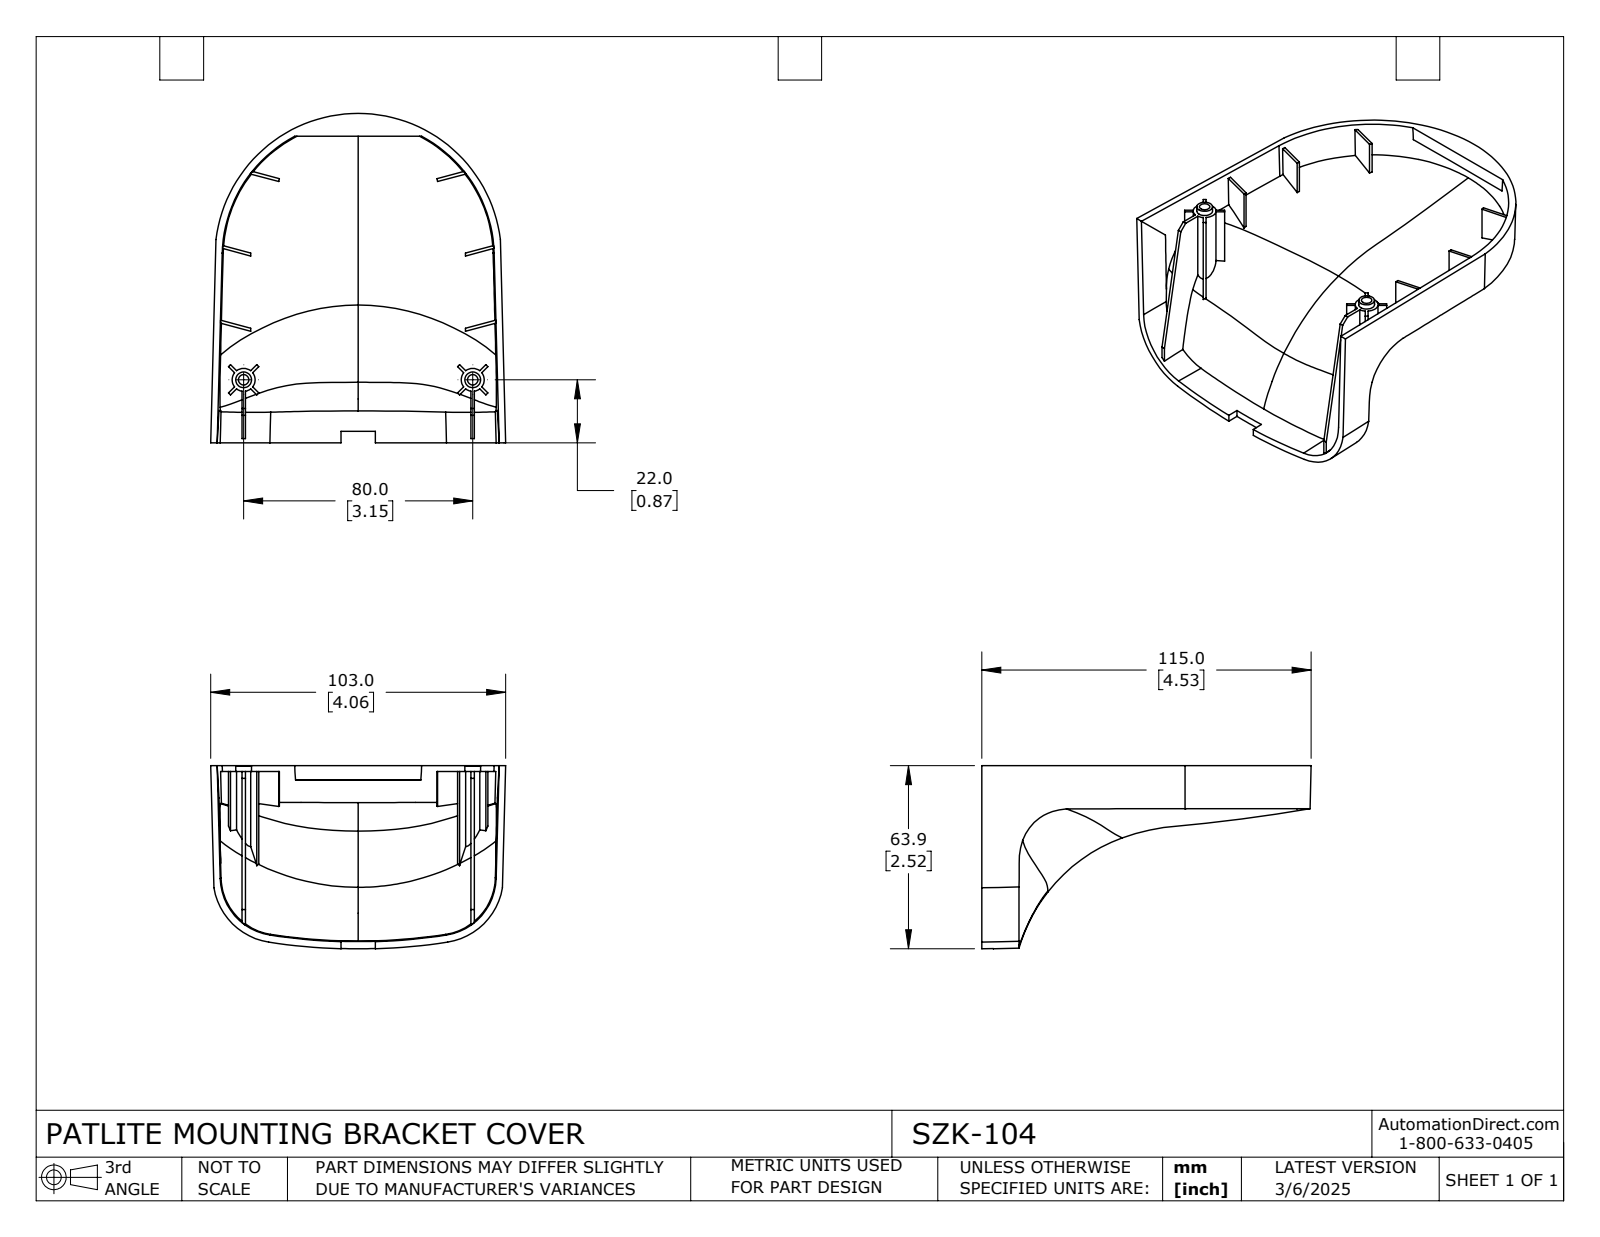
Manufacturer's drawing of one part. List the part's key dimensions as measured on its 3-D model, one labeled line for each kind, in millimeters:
Part name (STEP PRODUCT): SZK-104
STEP written by: SolidWorks 2024 (CONFIG_CONTROL_DESIGN)
Units: millimetres
Bodies: 1 solid, 122 faces (77 planar, 18 cylindrical, 27 other)
Overall size (bounding box): 115 × 103 × 63.91
Volume: 47 872 mm³ · Surface area: 42 552 mm²
Round holes (diameter × count): ⌀3.62 ×2
Round bosses / shafts (diameter × count): ⌀5.5 ×2
Partial cylindrical surfaces — rounded edges, fillets, slot ends (radius × count): R4 ×2
Main face-to-face distances: 2.29, 1.2, 80, 1, 2.28, 56.56, 78.8, 81.2, 27.64, 1.04
Hole centre spacings: 80
